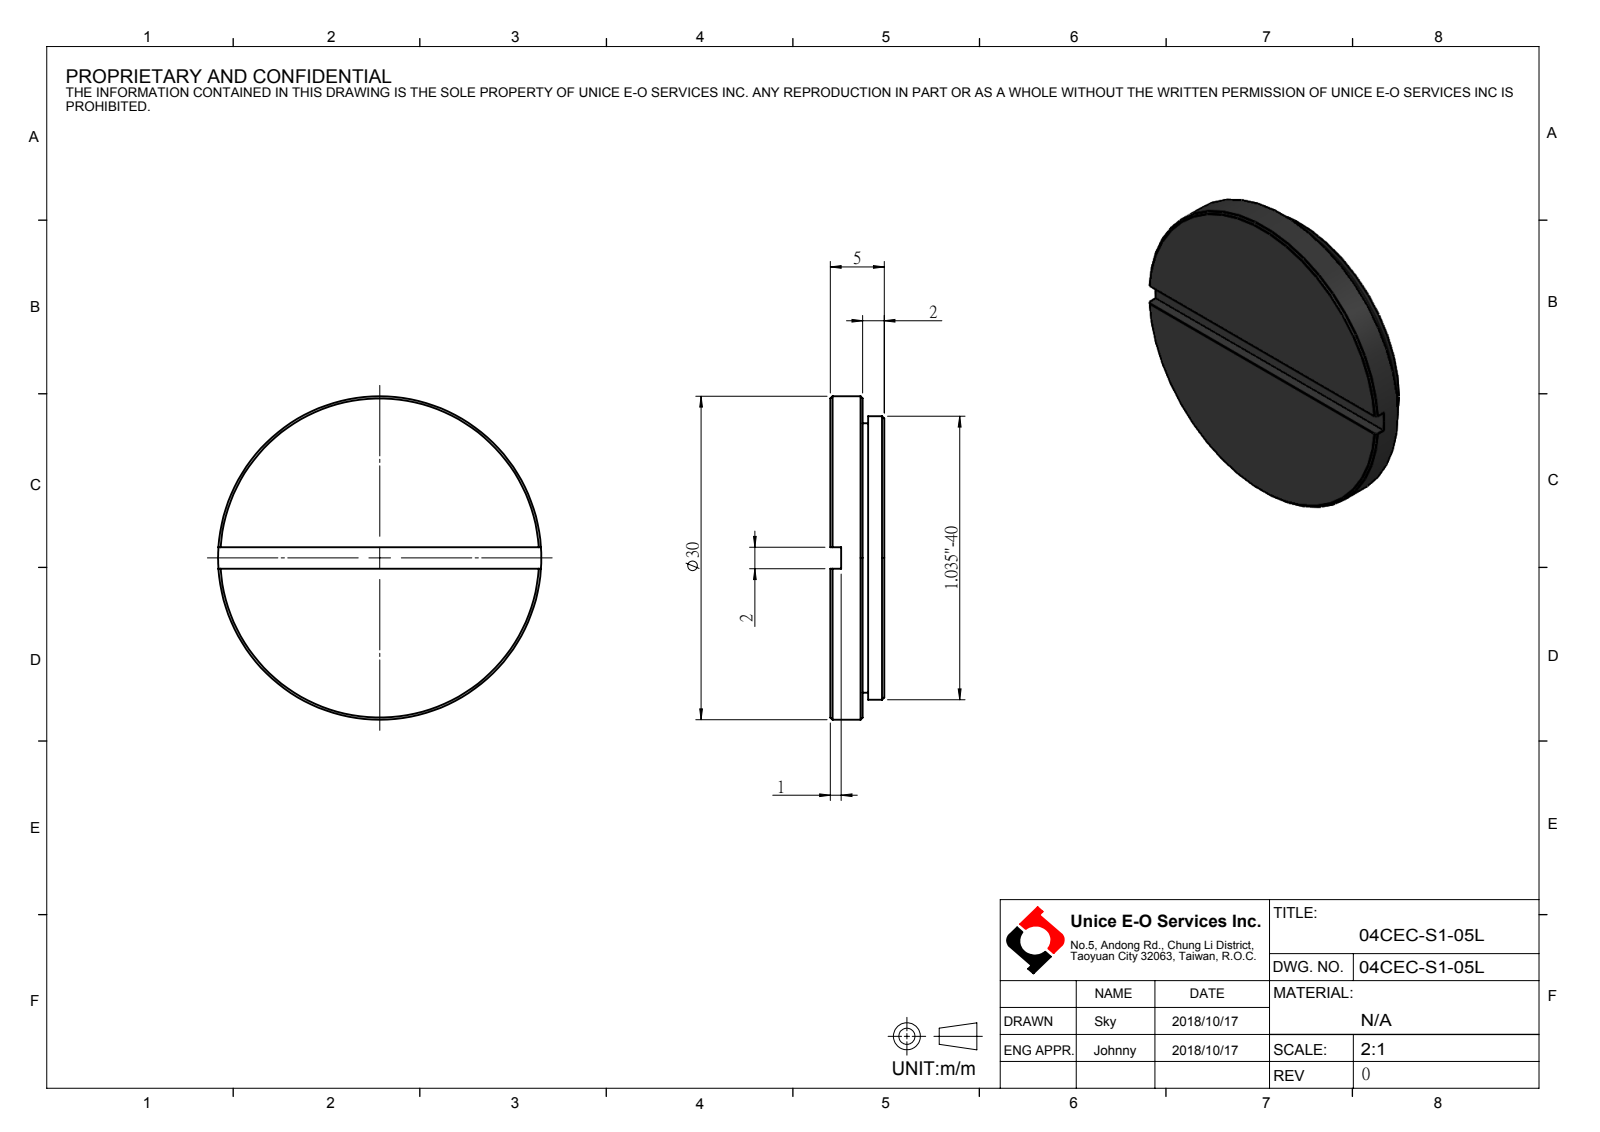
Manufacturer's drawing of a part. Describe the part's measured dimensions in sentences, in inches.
The part is named "04CEC-S1-05L". Its 3-D file was written by "SolidWorks 2016 (AUTOMOTIVE_DESIGN)". It is 0 solids with 19 faces: 7 planar, 6 cylindrical and 6 other. Overall it measures 1.181 by 1.181 by 0.197 inches. Round bosses or shafts: 1 of diameter 1.181, 1 of diameter 1.035, 1 of diameter 0.984. The main face-to-face distances are 0.197, 0.079, 0.118, 0.157, 0.039.
